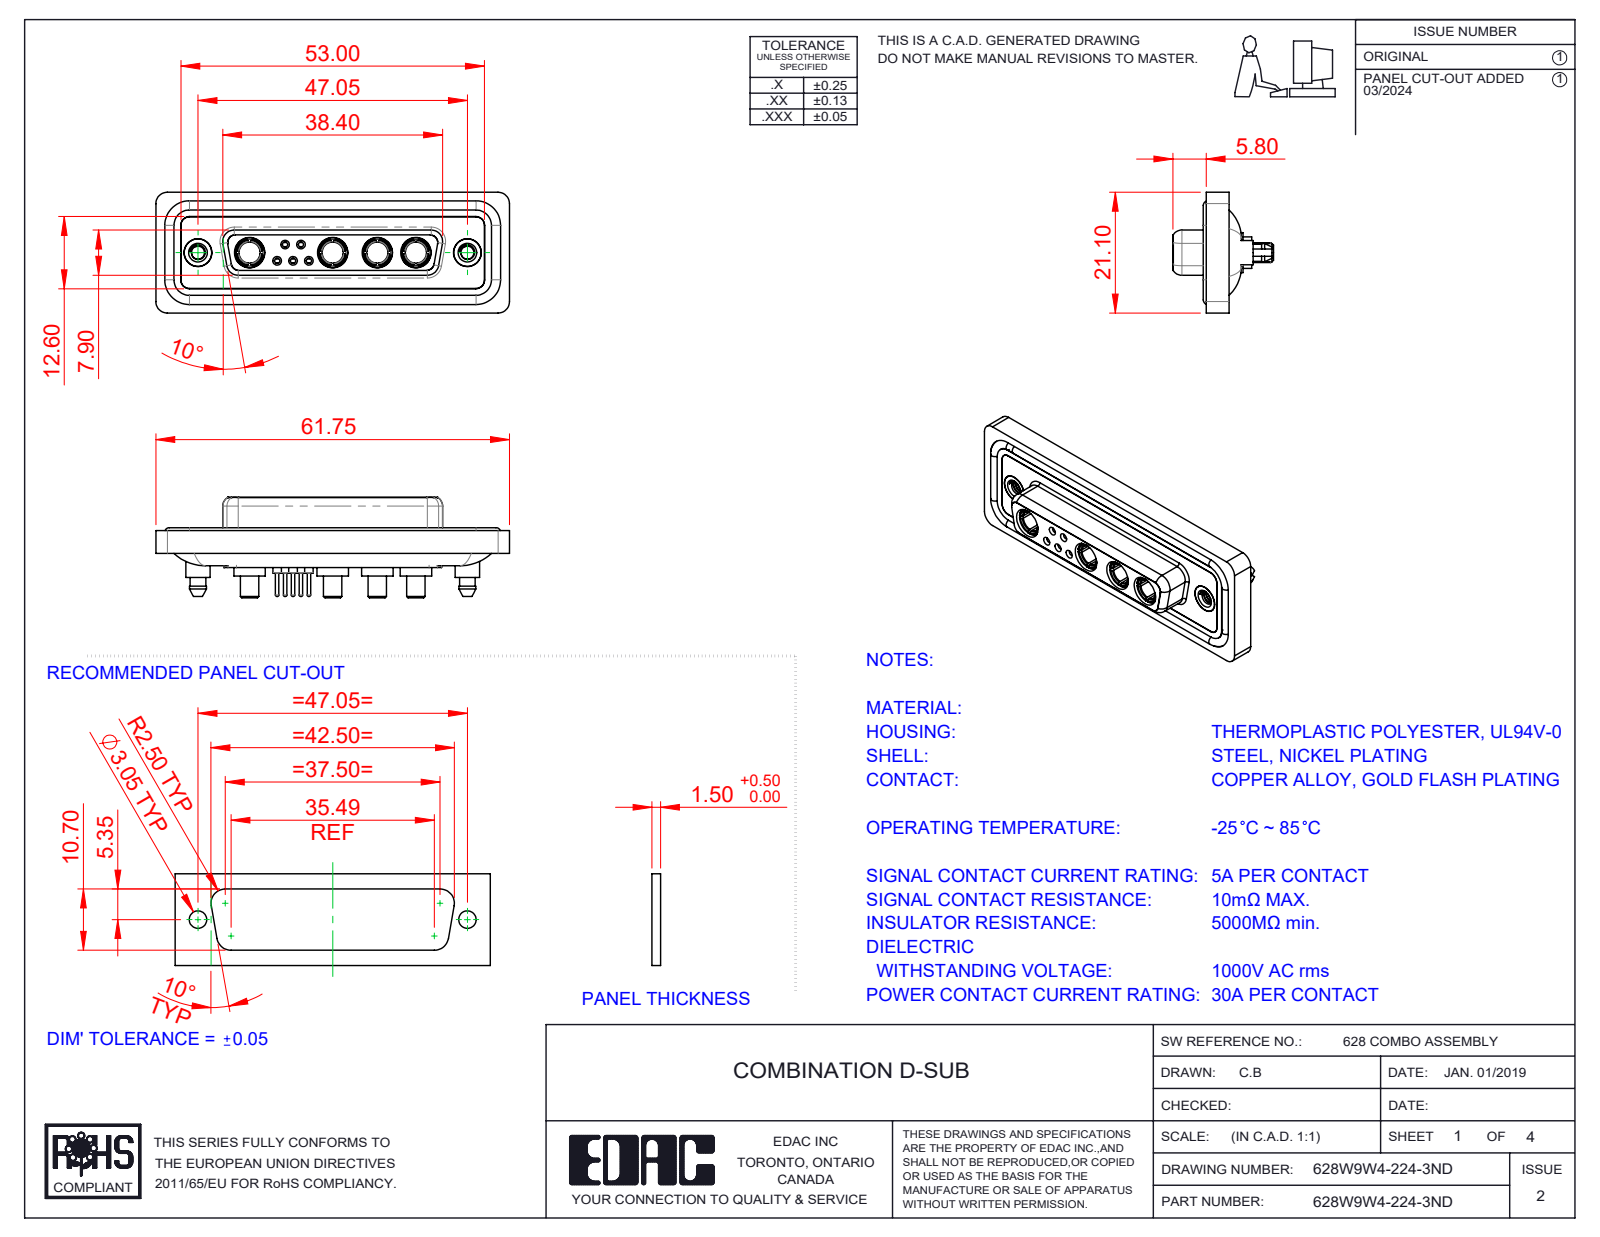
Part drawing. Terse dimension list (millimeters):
name: 628Combo Threaded Boardlock_D; 628Combo Shell Front_25 Contacts; 628Combo Contact Row 2_24; 628Combo Shell Rear_25 Contacts (+5 more)
written by: SolidWorks 2023 (CONFIG_CONTROL_DESIGN)
unit: mm
bodies: 20 solids, 1023 faces (312 planar, 423 cylindrical, 288 other)
size: 61.75 × 21.1 × 17.55
volume: 8 387 mm³; area: 13 920 mm²
holes: 6× ⌀4.85, 5× ⌀0.9, 5× ⌀1.1, 5× ⌀1.5, 5× ⌀2, 4× ⌀3.7, 4× ⌀5.3, 3× ⌀1.6, 2× ⌀1.7, 2× ⌀2.26, 2× ⌀4, 2× ⌀4.05
bosses: 6× ⌀1.6, 5× ⌀2.2, 5× ⌀0.6, 4× ⌀5.5, 4× ⌀5.2, 4× ⌀4.96, 4× ⌀4.75, 4× ⌀3.75
rounds: 24× R1.5, 18× R2, 10× R1.6, 8× R1.35, 4× R0.25, 4× R0.5, 4× R0.6, 4× R0.65
face distances: 0.4, 1.8, 7.45, 5.65, 0.5, 7.05, 6.6, 1.6, 1.1, 2.9
hole spacings: 3.16, 2.77, 5.03, 2.76, 4.4, 5.02, 5.54, 5.73
